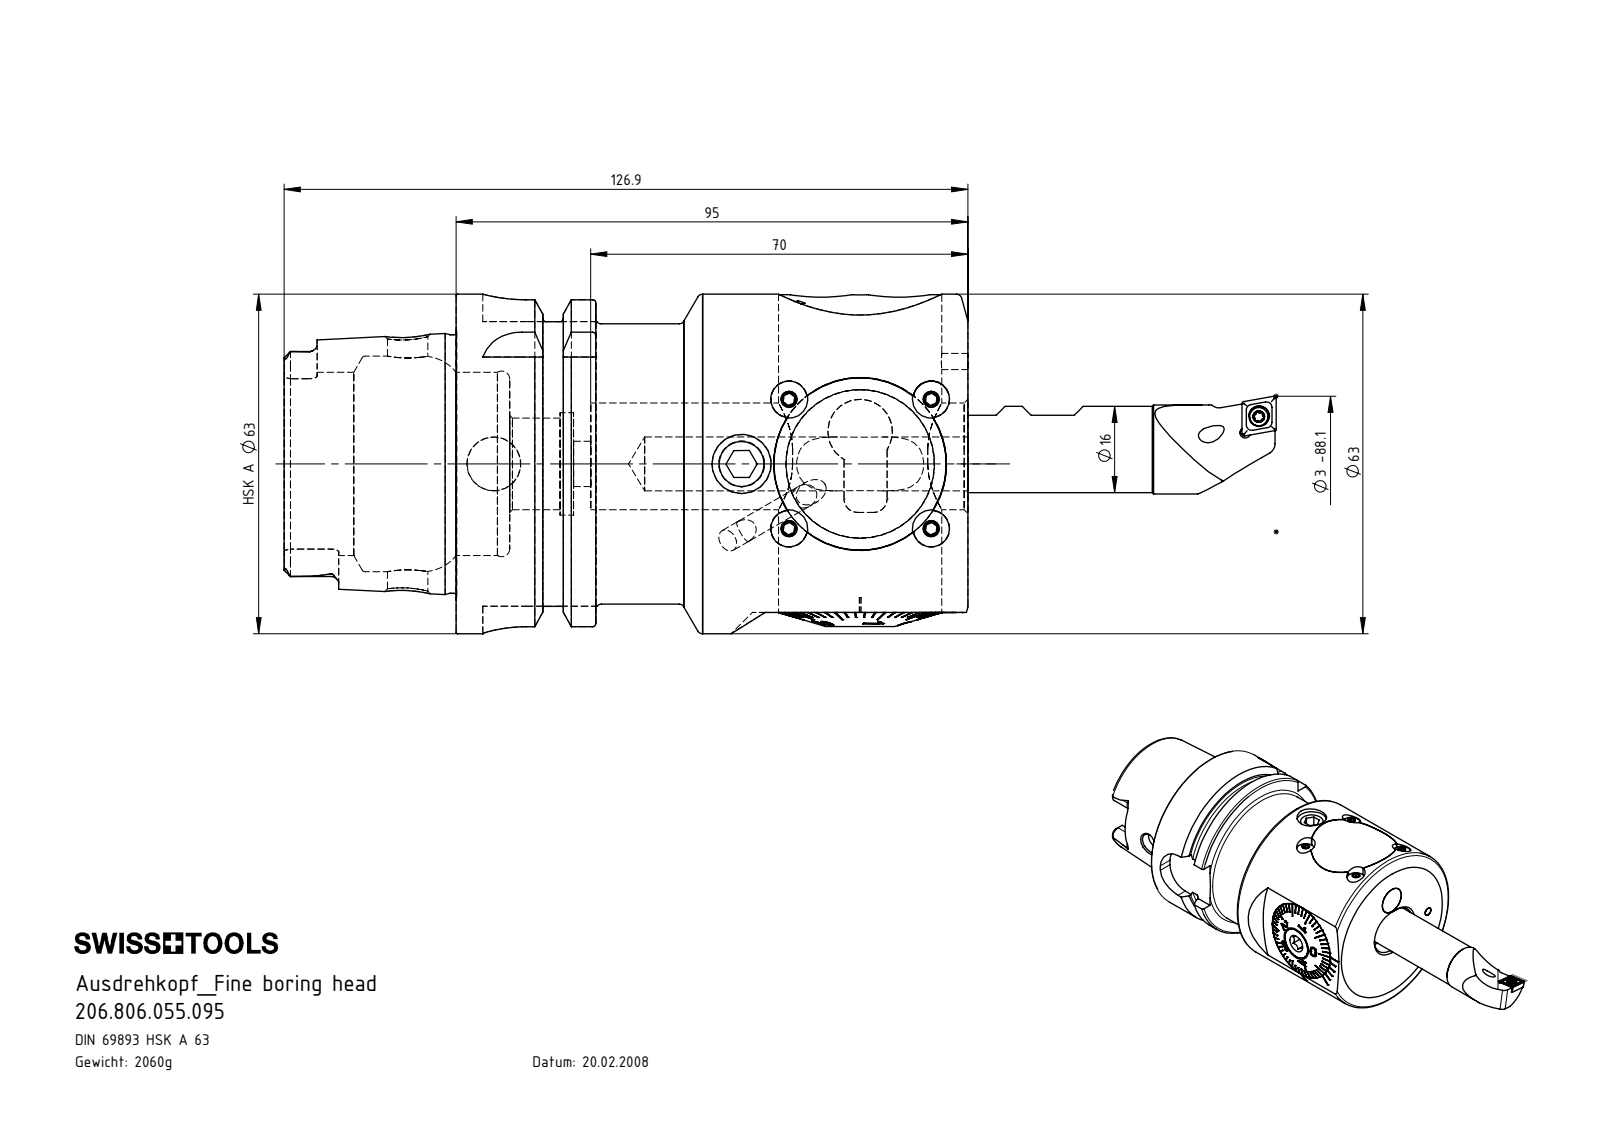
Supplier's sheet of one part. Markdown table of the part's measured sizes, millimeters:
| quantity | value |
| --- | --- |
| part name | 206.806.055.095; Glasmassstab; A63-ER5.001.006_A; Schutzhülle_eingebaut (+8 more) |
| STEP written by | SolidWorks 2017 (CONFIG_CONTROL_DESIGN) |
| units | millimeters |
| bodies | 43 solids, 1798 faces (761 planar, 394 cylindrical, 643 other) |
| overall size | 184.15 × 63 × 63 |
| volume | 265 306 mm³ |
| surface area | 90 719 mm² |
| round holes (diameter × count) | 1.6 × 6, 2.1 × 5, 2.5 × 4, 8.5 × 4, 3 × 2, 4.2 × 2, 2 × 1, 2.05 × 1, 2.8 × 1, 3.85 × 1, 6.8 × 1, 7.5 × 1 |
| round bosses / shafts (diameter × count) | 3 × 5, 10 × 4, 6.8 × 3, 27 × 2, 0.4 × 2, 63 × 1, 54.95 × 1, 52 × 1 |
| partial cylindrical surfaces (radius × count) | 1.5 × 28, 0.2 × 9, 0.21 × 6, 1.4 × 6, 0.36 × 5, 2.88 × 4, 3.5 × 4, 8 × 4 |
| main face-to-face distances | 6.3, 3, 1, 44.8, 95, 3.3, 7.3, 4.3, 43.8, 45.1 |
| hole center spacings | 11.63, 12.42, 17.84, 26.12, 7.25, 8.34, 10, 12.15 |
